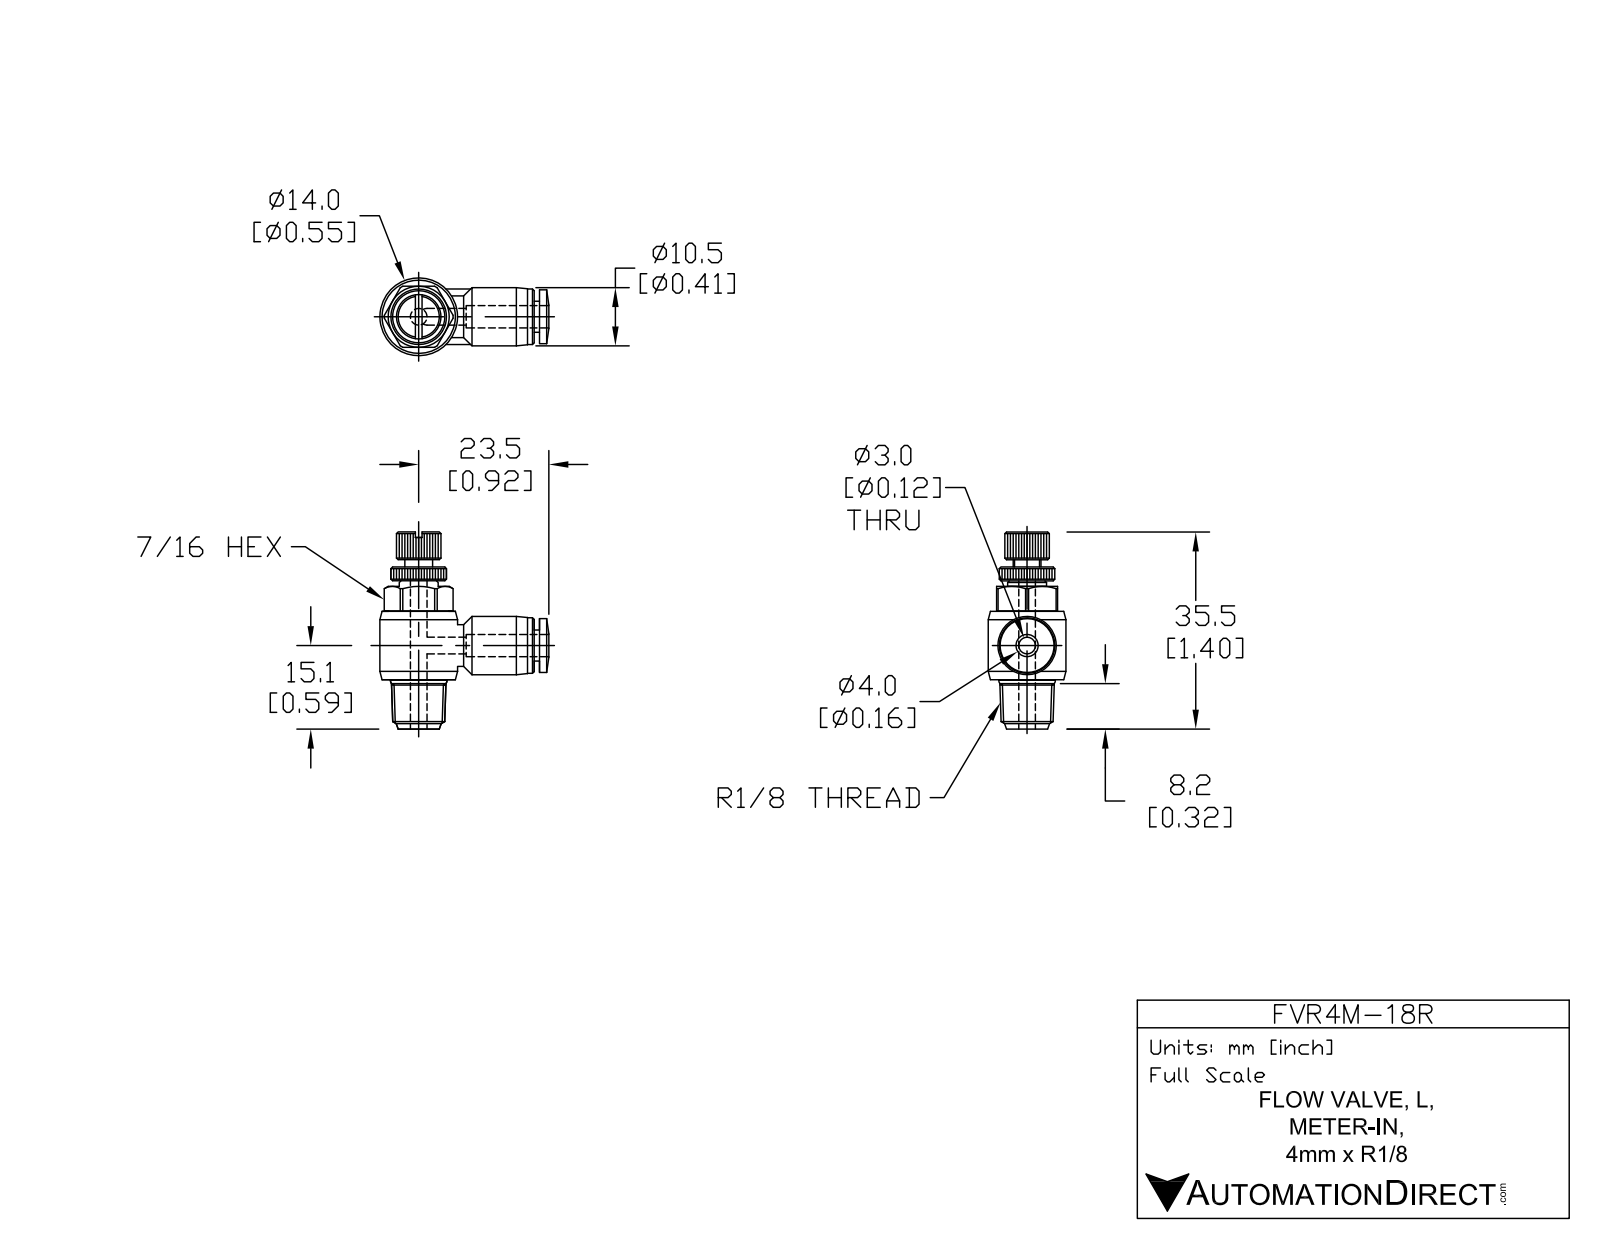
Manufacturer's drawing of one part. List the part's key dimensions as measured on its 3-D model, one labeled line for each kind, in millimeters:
Part name (STEP PRODUCT): FVR4M-18R
STEP written by: SolidWorks 2015 (AUTOMOTIVE_DESIGN)
Units: millimetres
Bodies: 1 solid, 492 faces (189 planar, 113 cylindrical, 190 other)
Overall size (bounding box): 40.7 × 30.5 × 14
Volume: 4 410 mm³ · Surface area: 2 855 mm²
Round holes (diameter × count): ⌀3 ×2, ⌀4.3 ×1
Round bosses / shafts (diameter × count): ⌀9.7 ×2, ⌀14 ×1, ⌀10.8 ×1, ⌀10.5 ×1, ⌀10 ×1, ⌀7.5 ×1, ⌀7 ×1, ⌀5.6 ×1
Partial cylindrical surfaces — rounded edges, fillets, slot ends (radius × count): R4 ×1, R5 ×1, R6.2 ×1
Main face-to-face distances: 11, 16.8, 5.2, 20.3, 3.5, 1, 12.3, 4.5, 8, 0.9
